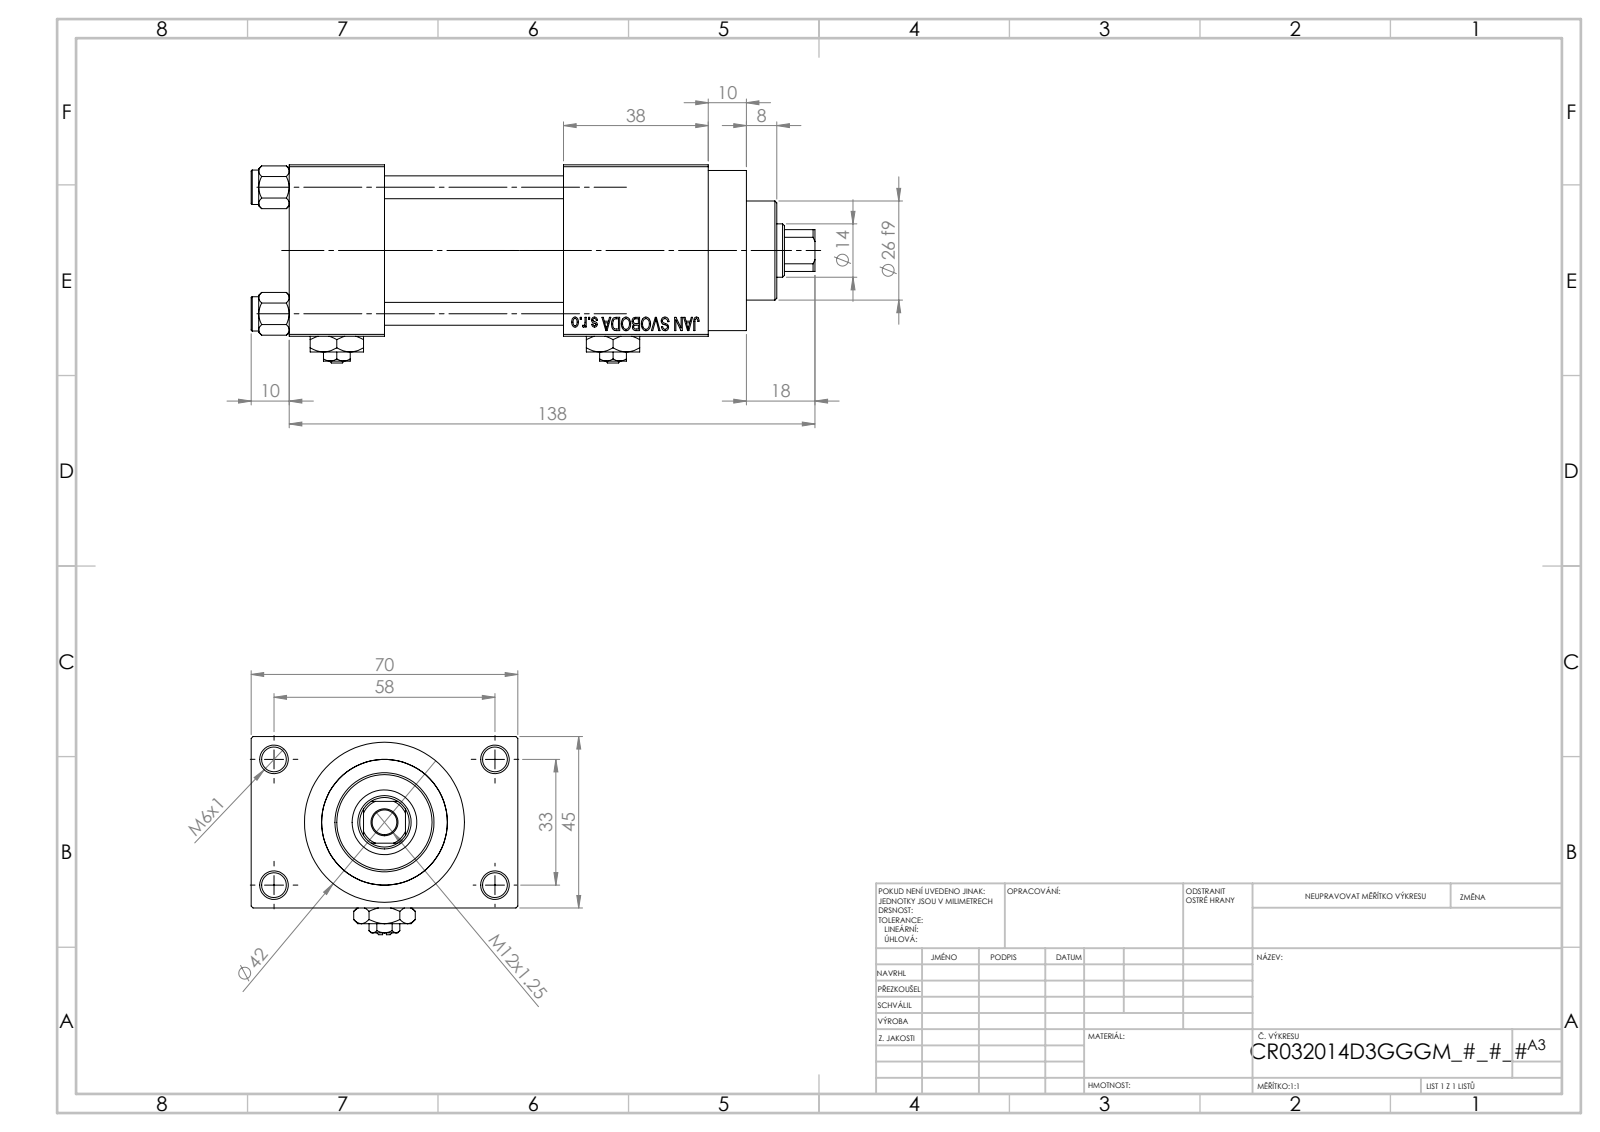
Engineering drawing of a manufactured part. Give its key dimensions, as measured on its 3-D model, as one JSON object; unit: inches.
{"part_name": "V215_VC_A; NUT_M5_D; V215CR_D_Body; V215CR_VCP_D (+2 more)", "step_written_by": "SolidWorks 2019 (CONFIG_CONTROL_DESIGN)", "units": "inches", "bodies": {"solids": 13, "faces": 1202, "planar": 542, "cylindrical": 100, "other": 560}, "overall_size": [5.827, 2.756, 2.047], "volume_in3": 13.76, "surface_area_in2": 116.6, "round_holes": [[0.256, 5], [0.236, 4], [0.276, 2], [0.518, 2], [0.787, 2], [0.551, 1], [0.669, 1], [0.945, 1], [1.26, 1], [1.299, 1]], "round_bosses_or_shafts": [[0.354, 4], [1.654, 1], [1.496, 1], [1.024, 1]], "partial_cylinders_radius": [[0.256, 1]], "face_to_face_distances": [1.772, 0.492, 2.264, 1.85, 0.984, 2.835, 2.756, 1.496, 3.346, 4.331], "hole_center_spacings": [0.488, 0.924, 1.307, 1.314, 1.392, 1.795, 2.219, 1.299]}
